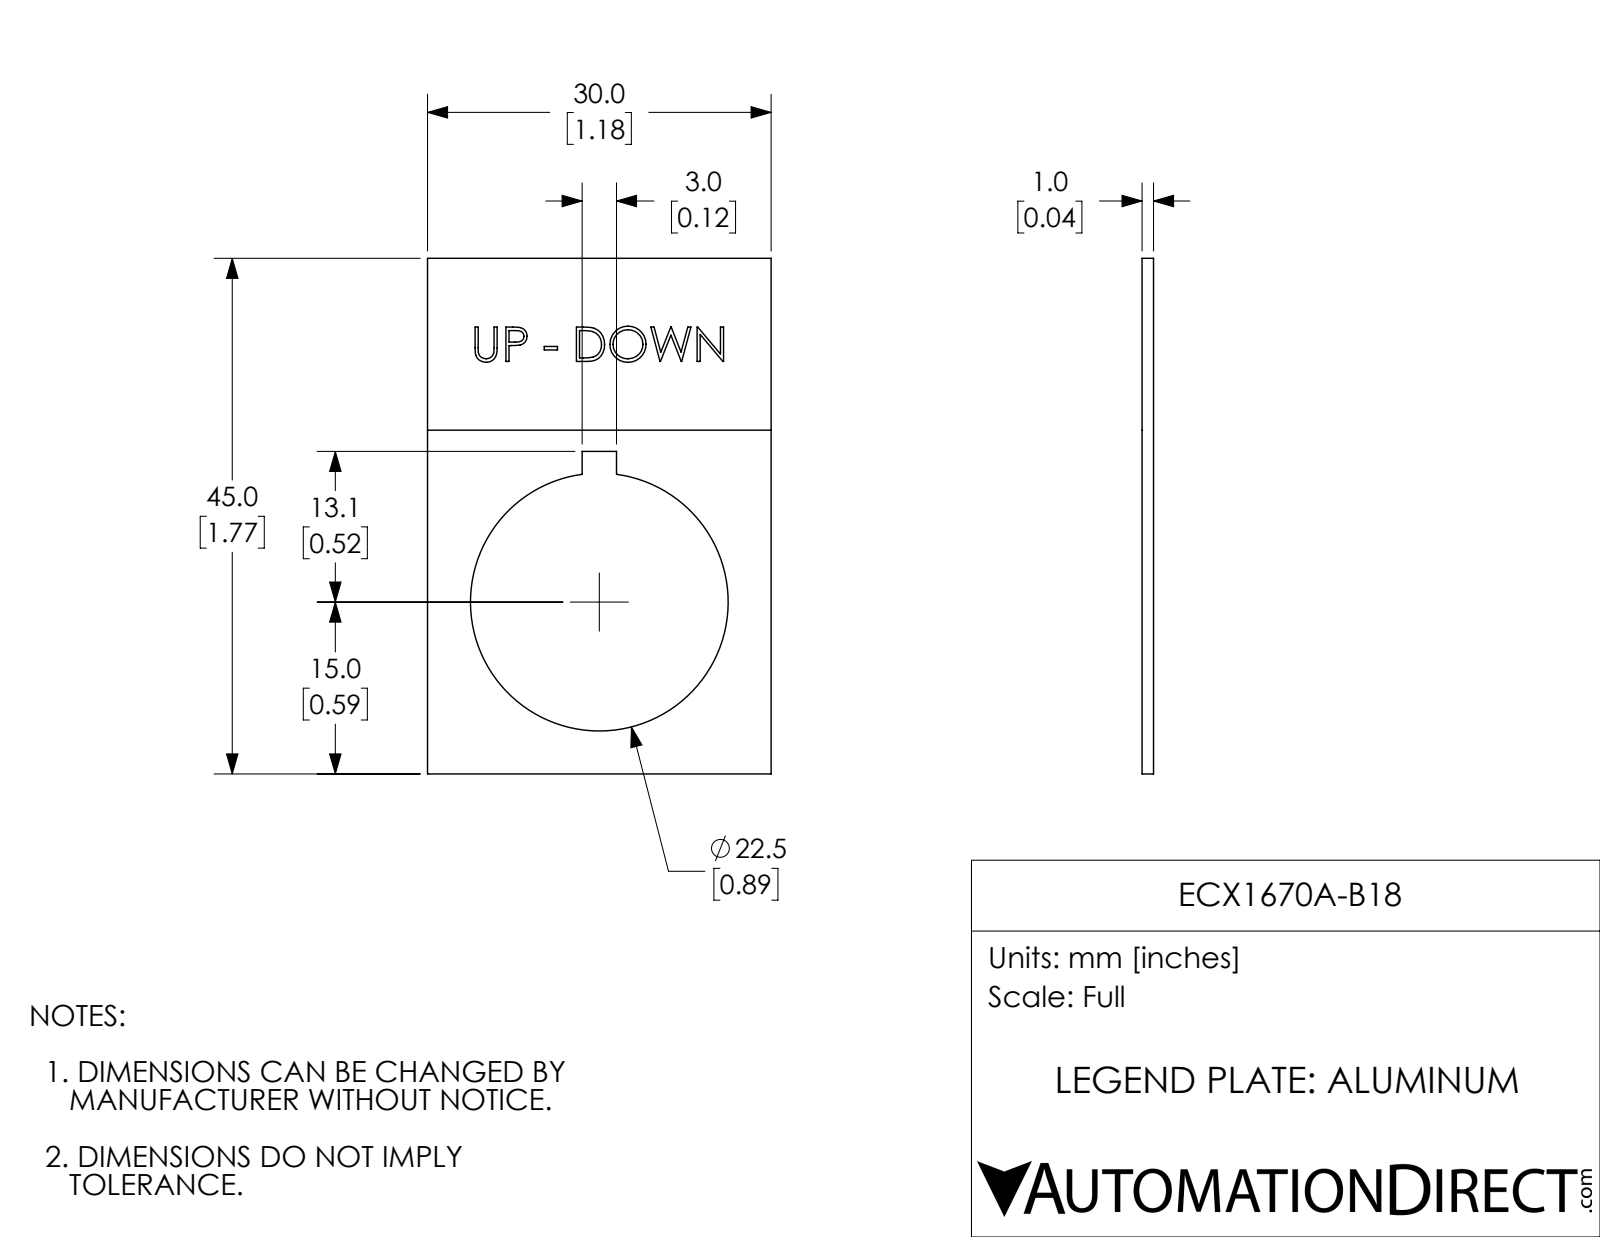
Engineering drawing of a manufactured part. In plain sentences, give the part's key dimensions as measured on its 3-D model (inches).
The part is named "ECX1670A-B18". Its 3-D file was written by "SolidWorks 2017 (AUTOMOTIVE_DESIGN)". It is 1 solid with 98 faces: 67 planar, 3 cylindrical and 28 other. Overall it measures 1.772 by 1.181 by 0.039 inches. Its volume is 0.058 cubic inches and its surface area 3.287 square inches. Round holes: 1 of diameter 0.886. The main face-to-face distances are 0.039, 1.181, 1.772, 0.038, 0.531, 0.65, 1.108, 0.663, 0.118, 0.415.
